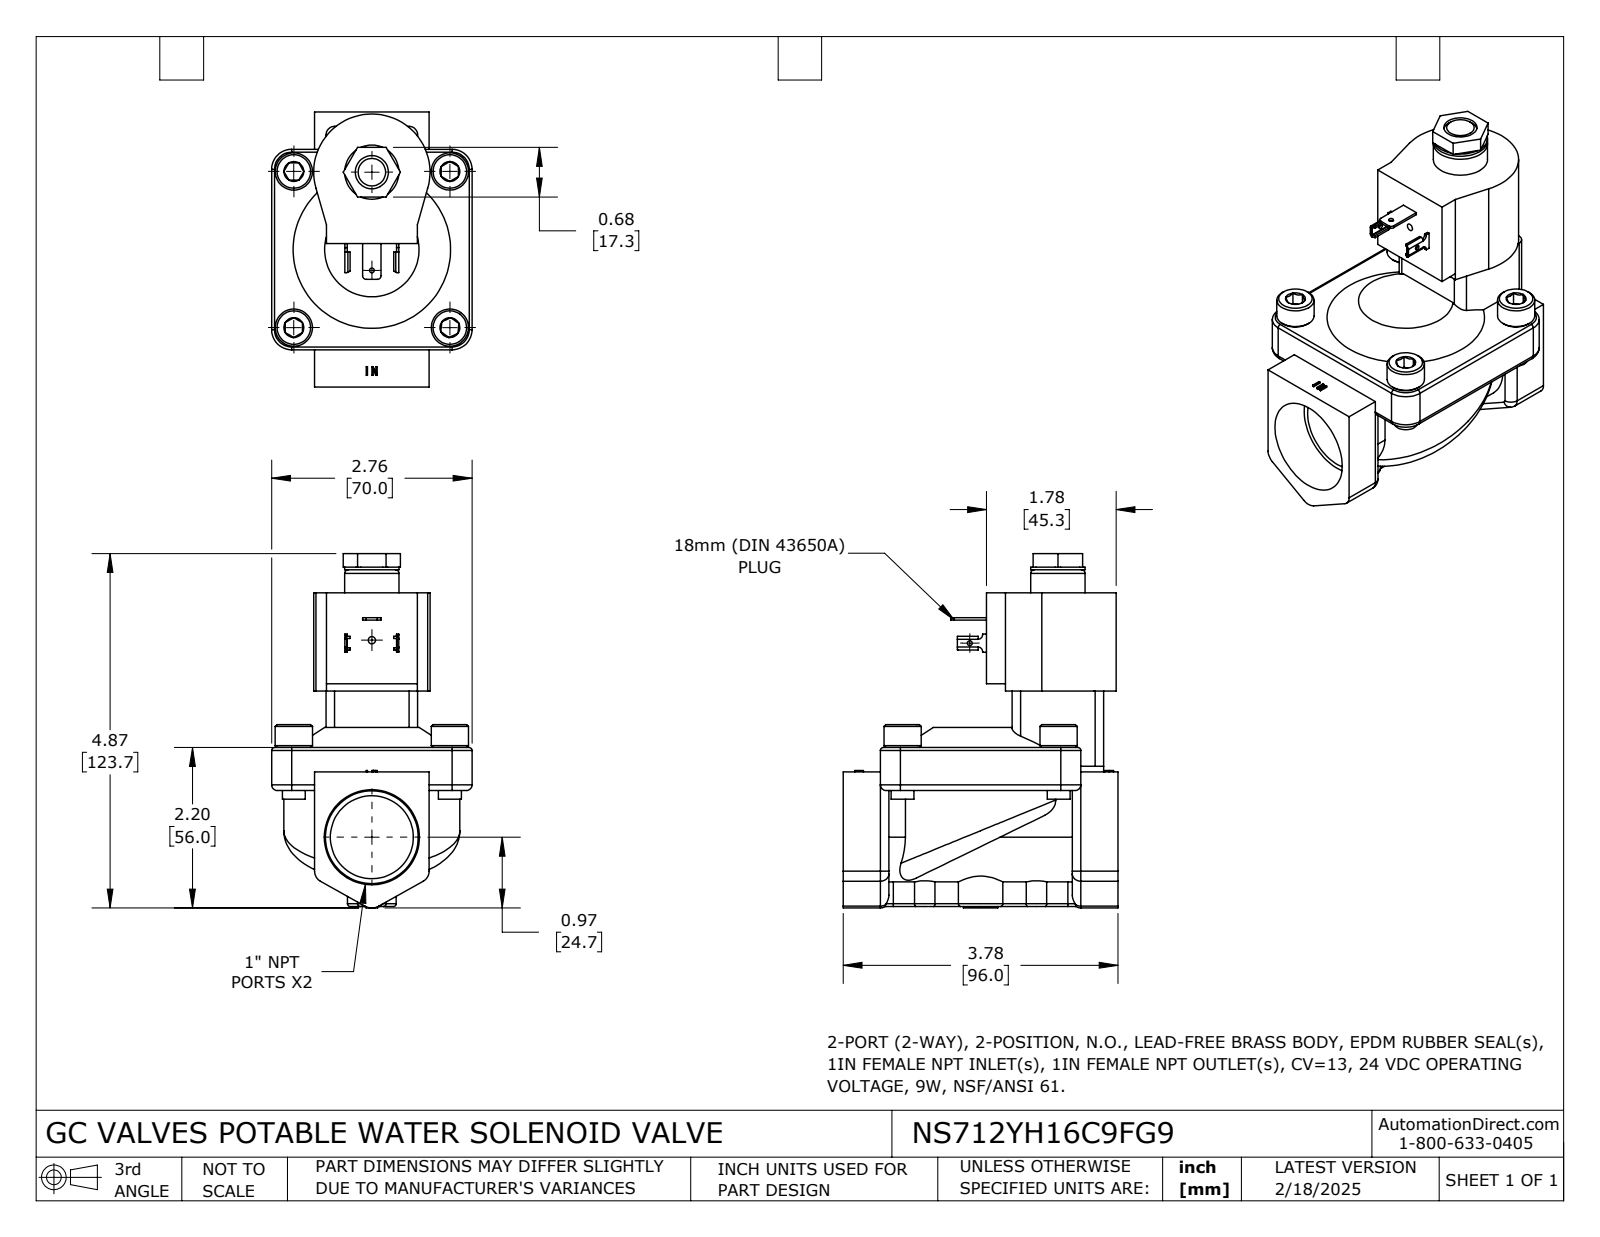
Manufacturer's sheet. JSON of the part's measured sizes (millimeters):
{"part_name": "NS712YH16C9FG9", "step_written_by": "SolidWorks 2024 (CONFIG_CONTROL_DESIGN)", "units": "millimeters", "bodies": {"solids": 1, "faces": 409, "planar": 196, "cylindrical": 112, "other": 101}, "overall_size": [123.71, 96, 70], "volume_mm3": 256002, "surface_area_mm2": 45150, "round_holes": [[1.68, 1], [1.7, 1], [2.53, 1], [11.58, 1], [28.98, 1]], "round_bosses_or_shafts": [[13, 4], [8, 4], [18.95, 1]], "partial_cylinders_radius": [[3, 12], [1, 6], [0.15, 4], [1.04, 4], [2, 4], [7, 4], [5, 3], [1.27, 2]], "face_to_face_distances": [15, 4, 36, 53.99, 19, 51, 55, 32, 7, 6.5], "hole_center_spacings": [34.29, 68.76]}
